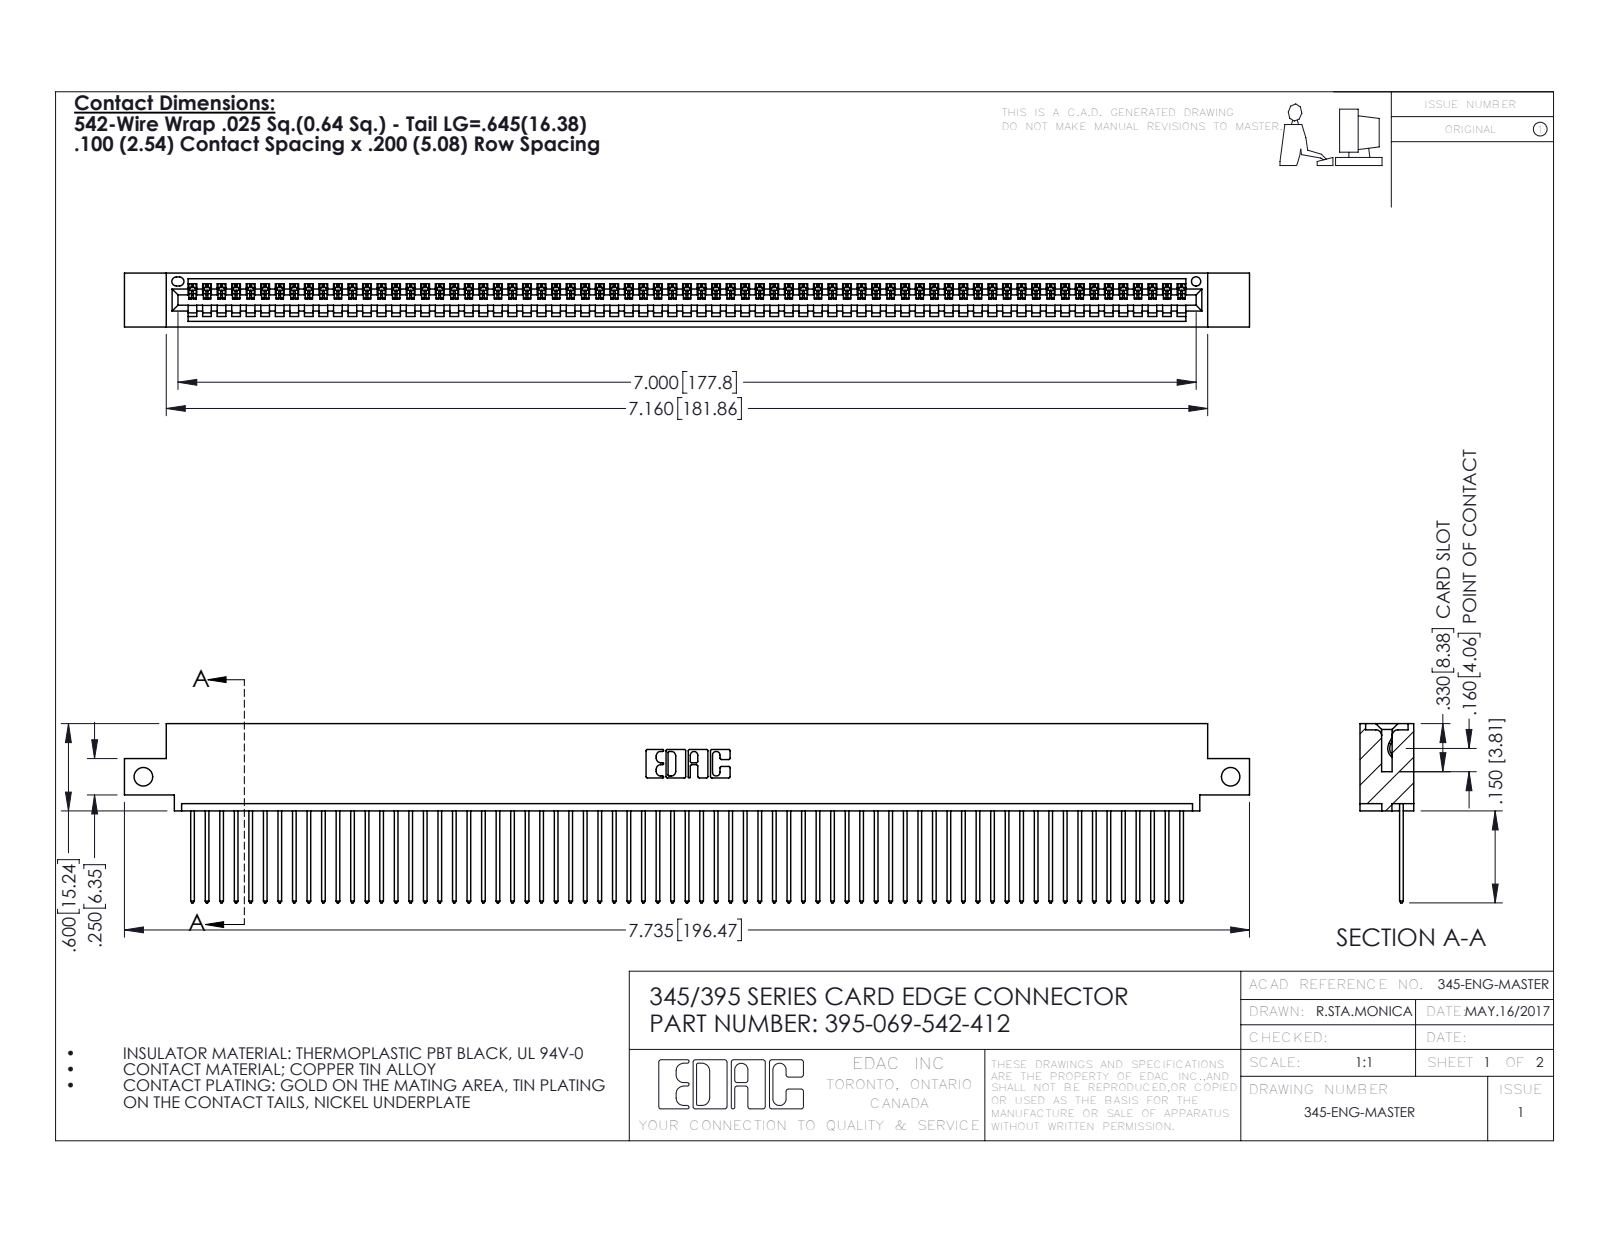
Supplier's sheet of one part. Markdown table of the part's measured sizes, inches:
| quantity | value |
| --- | --- |
| part name | 395-069-542-412; 345-292-001_345-293-142; 345 Part_0.110 Offset - Side Mount |
| STEP written by | SolidWorks 2016 (CONFIG_CONTROL_DESIGN) |
| units | inches |
| bodies | 70 solids, 4132 faces (2844 planar, 1288 cylindrical, 0 other) |
| overall size | 7.735 × 1.232 × 0.37 |
| volume | 1.152 in³ |
| surface area | 40.86 in² |
| round holes (diameter × count) | 0.128 × 2, 0.064 × 1 |
| partial cylindrical surfaces (radius × count) | 0.006 × 138, 0.01 × 138, 0.01 × 22, 0.007 × 6, 0.031 × 6, 0.026 × 3, 0.031 × 2, 0.04 × 2 |
| main face-to-face distances | 0.072, 0.298, 0.098, 0.272, 0.025, 0.37, 0.2, 0.225, 0.149, 0.072 |
| hole center spacings | 7.475 |
